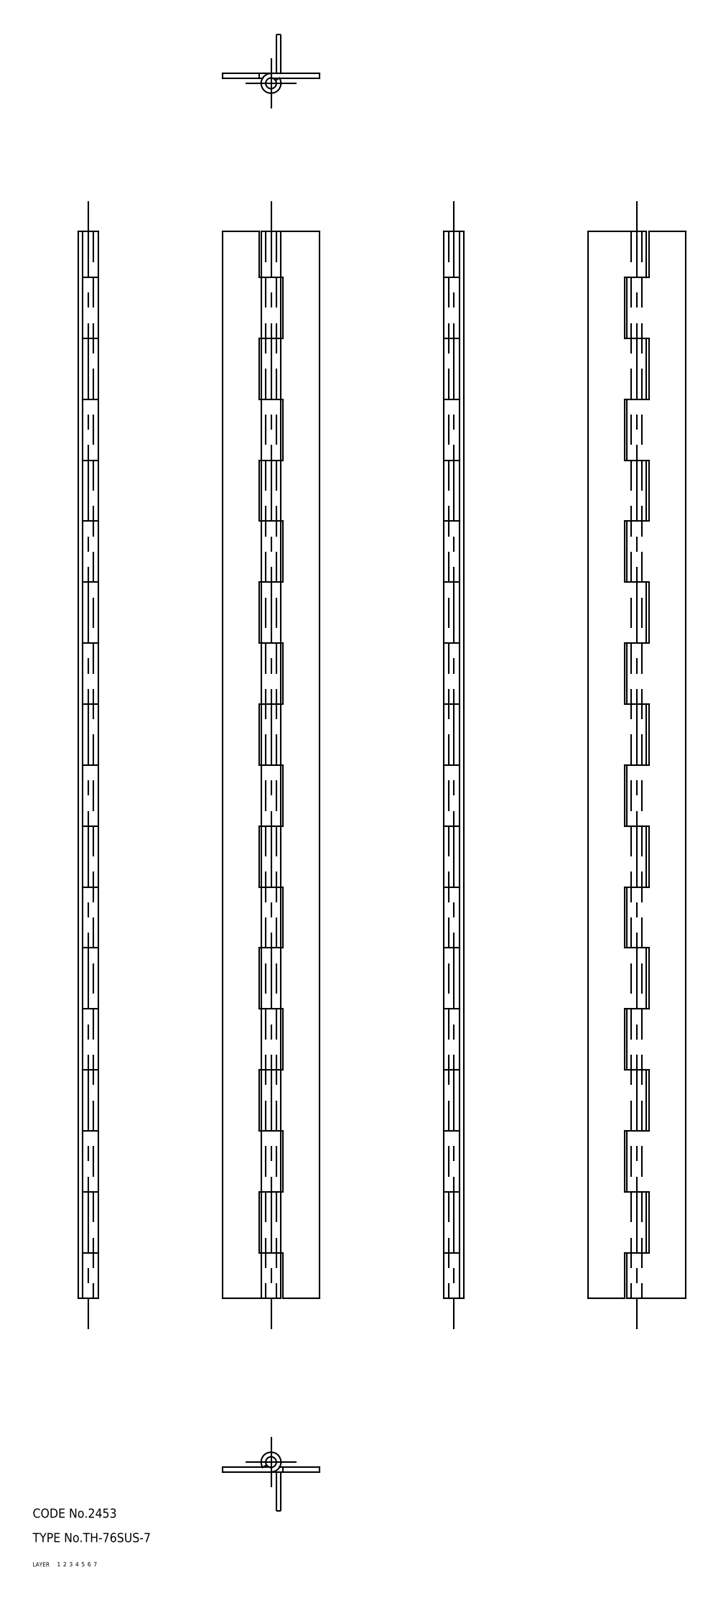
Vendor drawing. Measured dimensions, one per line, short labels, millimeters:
name: shaft; hinge piece_B; hinge piece_A; TH_76SUS_7_15776_36
written by: CADfix (AUTOMOTIVE_DESIGN)
unit: mm
bodies: 3 solids, 120 faces (0 planar, 0 cylindrical, 120 other)
size: 350 × 32 × 6.5
volume: 24 982 mm³; area: 35 780 mm²
